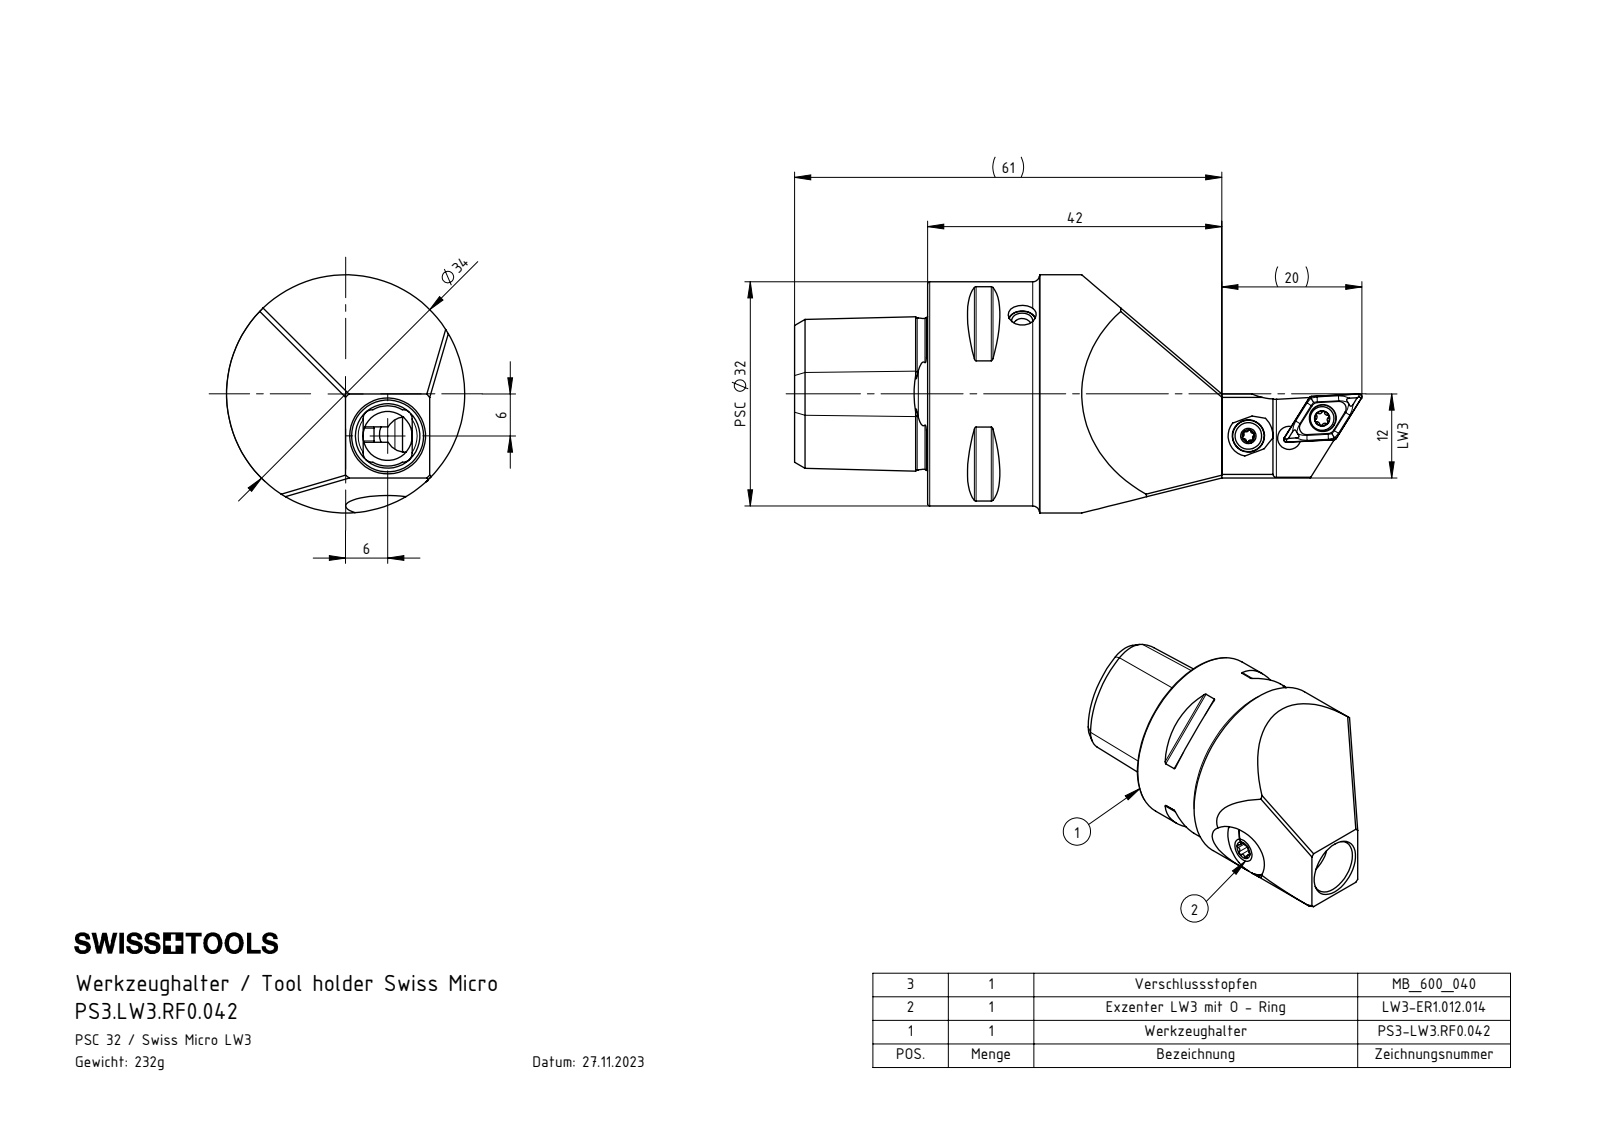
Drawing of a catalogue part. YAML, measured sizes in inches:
part_name: "KVT_MB_600_040; PS3.LW3.RF0.042; LW3-ER1.012.014_E_Standard<Wie bearbeitet>; DIN 3771 - 7x1 (+2 more)"
step_written_by: "SolidWorks 2017 (AUTOMOTIVE_DESIGN)"
units: inches
bodies: {solids: 6, faces: 318, planar: 65, cylindrical: 99, other: 154}
overall_size: [2.402, 1.339, 1.339]
volume: 1.805
surface_area: 15.2
round_holes:
  - {diameter: 0.13, count: 2}
  - {diameter: 0.157, count: 2}
  - {diameter: 0.039, count: 1}
  - {diameter: 0.094, count: 1}
  - {diameter: 0.118, count: 1}
  - {diameter: 0.142, count: 1}
  - {diameter: 0.276, count: 1}
  - {diameter: 0.363, count: 1}
  - {diameter: 0.402, count: 1}
  - {diameter: 0.472, count: 1}
  - {diameter: 0.591, count: 1}
  - {diameter: 0.65, count: 1}
round_bosses_or_shafts:
  - {diameter: 1.339, count: 1}
  - {diameter: 1.26, count: 1}
  - {diameter: 0.449, count: 1}
  - {diameter: 0.374, count: 1}
  - {diameter: 0.303, count: 1}
  - {diameter: 0.157, count: 1}
partial_cylinders:
  - {radius: 0.012, count: 8}
  - {radius: 0.013, count: 6}
  - {radius: 0.023, count: 6}
  - {radius: 0.051, count: 4}
  - {radius: 0.098, count: 2}
  - {radius: 0.118, count: 1}
  - {radius: 0.142, count: 1}
  - {radius: 0.146, count: 1}
face_to_face_distances: [0.043, 0.748, 0.473, 0.465, 1.114, 2.402, 1.654, 0.358, 0.402, 0.059]
hole_center_spacings: [0.334, 0.669]
